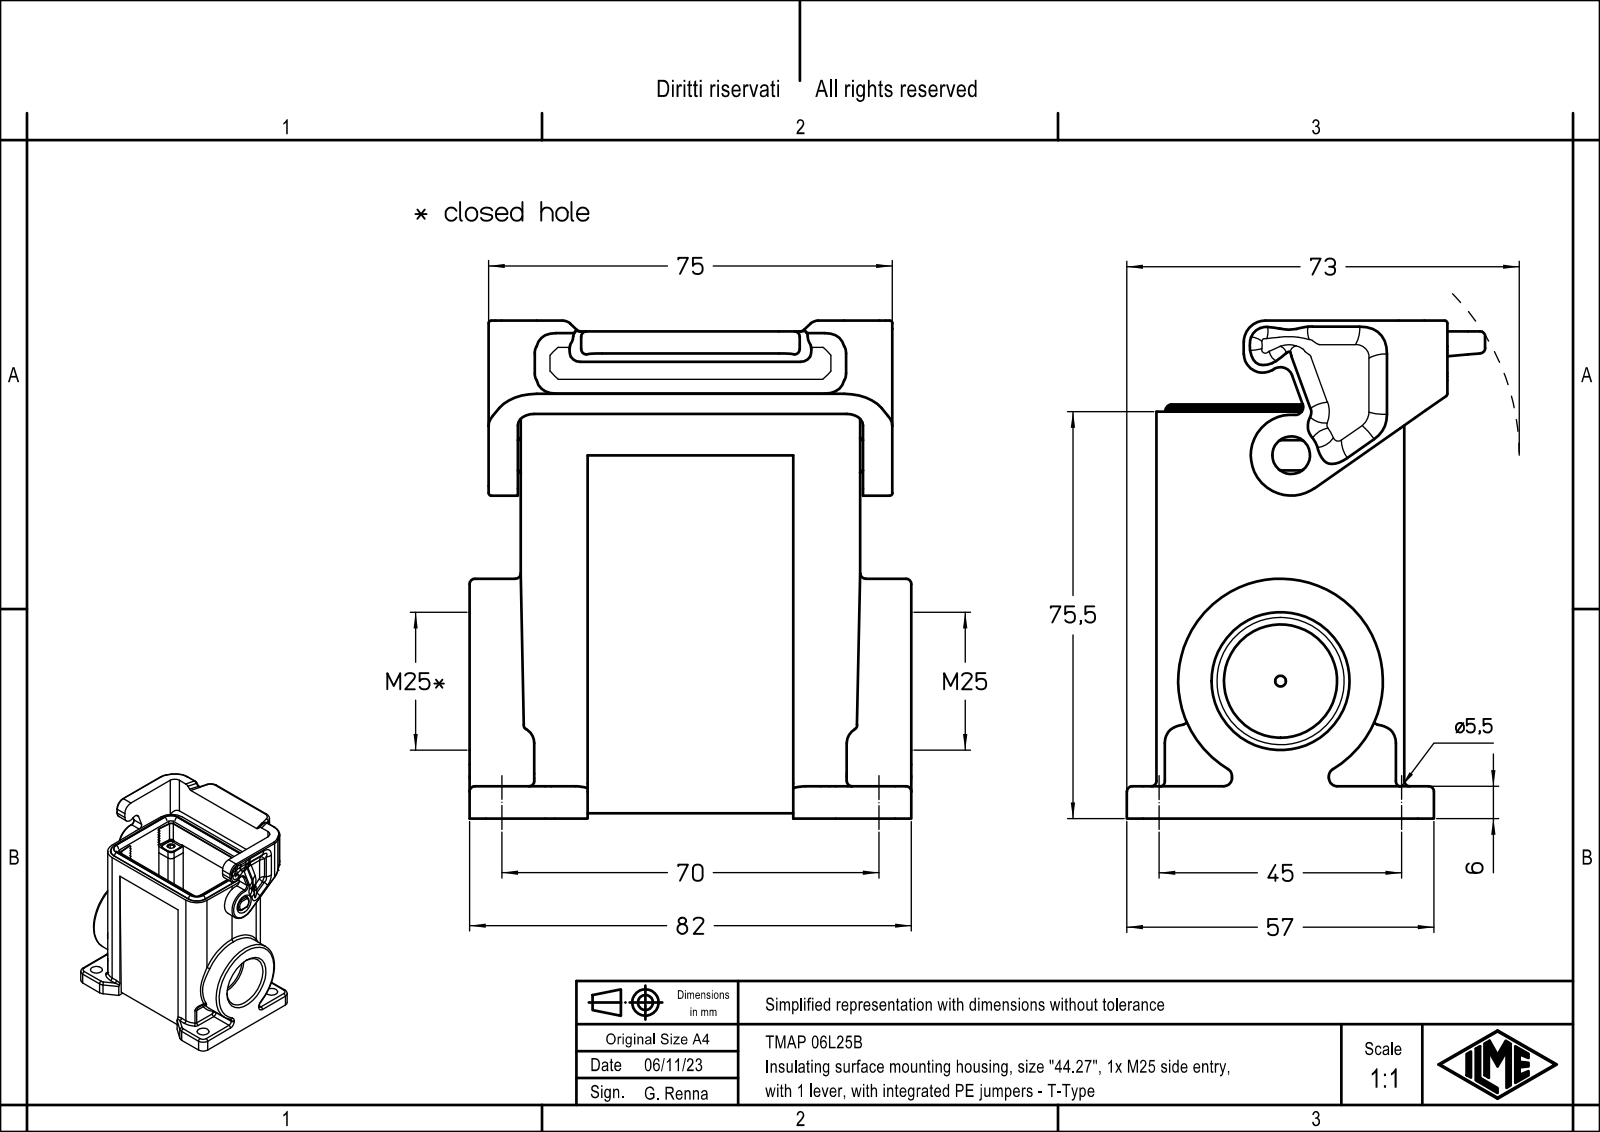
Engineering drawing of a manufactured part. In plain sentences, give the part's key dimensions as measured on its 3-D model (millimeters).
The part is named "TMAP 06L25B". Its 3-D file was written by "Creo Elements/Direct Modeling 20.1B 02-Apr-2019 (C) Parametric Technology GmbH (AUTOMOTIVE_DESIGN)". It is 1 solid with 518 faces: 318 planar, 164 cylindrical and 36 other. Overall it measures 92.4 by 82 by 66.5 millimeters. Its volume is 138 676 cubic millimeters and its surface area 50 113 square millimeters. Round holes: 4 of diameter 3.5, 4 of diameter 5.5, 1 of diameter 21, 1 of diameter 23.6. Round bosses or shafts: 1 of diameter 38. Partial cylindrical surfaces (rounded edges, fillets, slot ends): 17 of radius 1.5, 17 of radius 3, 14 of radius 2, 12 of radius 1.3, 8 of radius 1, 6 of radius 0.5, 4 of radius 1.6, 4 of radius 6. The main face-to-face distances are 5.4, 40.6, 46, 35.2, 5.5, 14.9, 1, 9, 67.1, 58.1. The hole center spacings are 15.81, 38.28, 57.71, 67.42, 27, 44, 45, 51.62.
